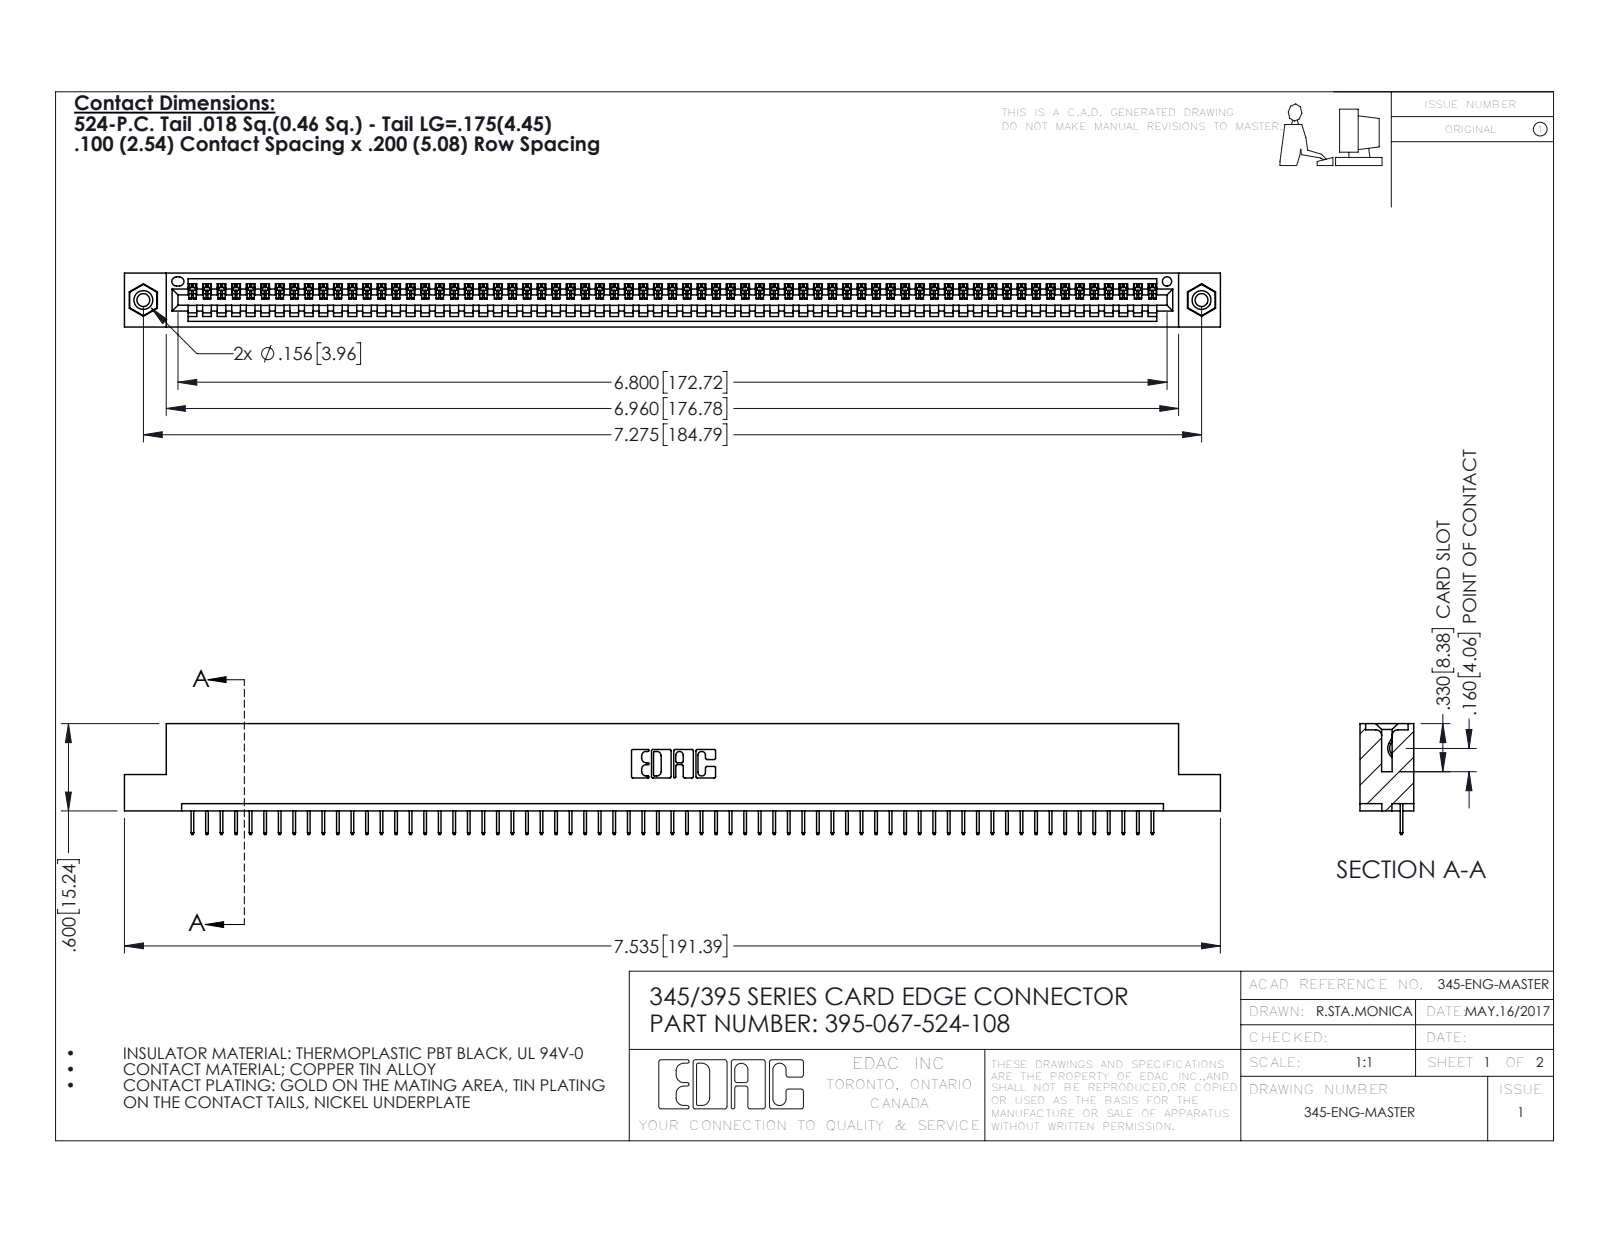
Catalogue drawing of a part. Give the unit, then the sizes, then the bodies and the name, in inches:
Units: inches
Overall size (bounding box): 7.535 × 0.762 × 0.37
Round holes (diameter × count): ⌀0.089 ×2, ⌀0.125 ×2, ⌀0.156 ×2, ⌀0.064 ×1
Round bosses / shafts (diameter × count): ⌀0.155 ×2
Partial cylindrical surfaces — rounded edges, fillets, slot ends (radius × count): R0.006 ×134, R0.01 ×22, R0.007 ×6, R0.031 ×6, R0.026 ×3, R0.031 ×2, R0.04 ×2, R0.014 ×1
Main face-to-face distances: 0.072, 0.298, 0.37, 0.2, 0.098, 0.272, 0.025, 0.225, 0.072, 0.149
Hole centre spacings: 0.27, 7.039, 7.275
Volume: 1.105 in³ · Surface area: 36.55 in²
Bodies: 70 solids, 4340 faces (3194 planar, 1130 cylindrical, 16 other)
Part name (STEP PRODUCT): 395-067-524-108; 345-250-001_345-250-003-102; 345 Part_Flush Mounting Lugs - 0.156 Dia-TI; 345-292-001_345-293-124
STEP written by: SolidWorks 2016 (CONFIG_CONTROL_DESIGN)
